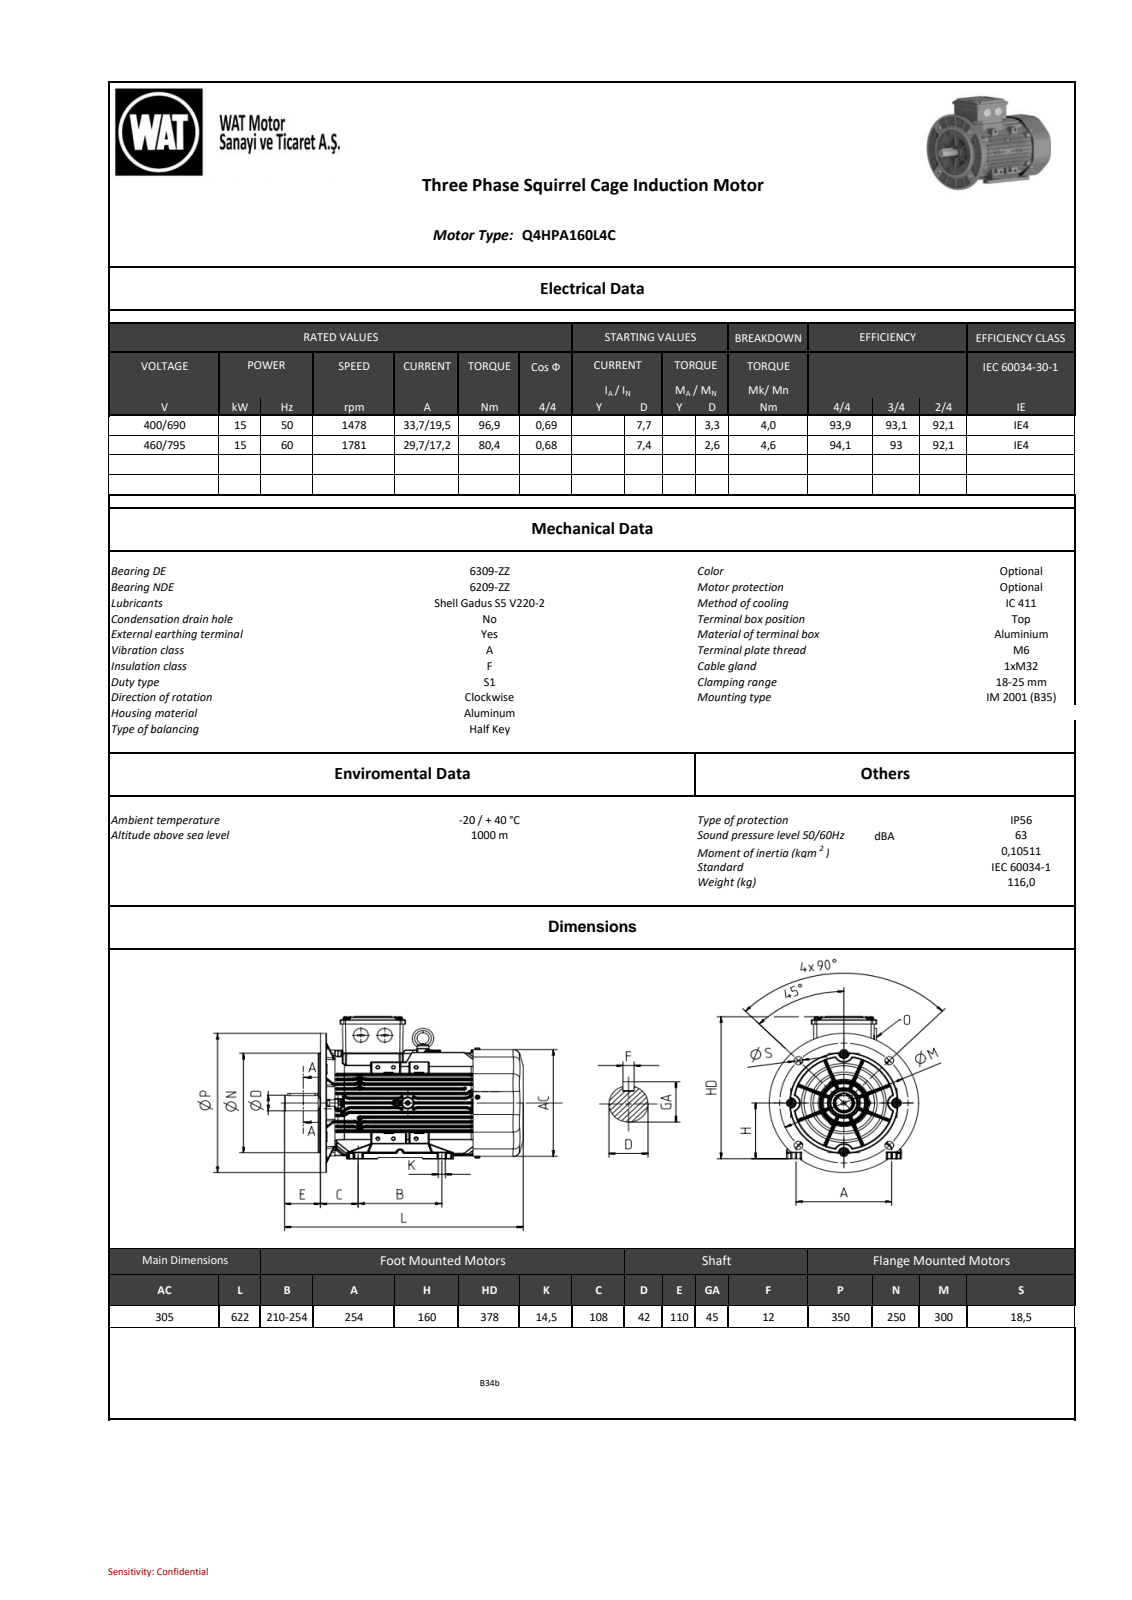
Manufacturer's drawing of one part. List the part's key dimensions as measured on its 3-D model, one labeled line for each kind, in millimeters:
Part name (STEP PRODUCT): AA_objects
STEP written by: SIEMENS PLM Software NX2206.8101 (AP203_CONFIGURATION_CONTROLLED_3D_DESIGN_OF_MECHANICAL_PARTS_AND_ASSEMBLIES_MIM_LF)
Units: millimetres
Bodies: 0 solids, 8586 faces (2343 planar, 3221 cylindrical, 3022 other)
Overall size (bounding box): 618.92 × 392.75 × 350
Round holes (diameter × count): ⌀15 ×4, ⌀10 ×1, ⌀14 ×1, ⌀17 ×1, ⌀72 ×1, ⌀85.63 ×1, ⌀94 ×1, ⌀114 ×1, ⌀134 ×1, ⌀154 ×1, ⌀174 ×1, ⌀194 ×1
Round bosses / shafts (diameter × count): ⌀16 ×4, ⌀10 ×4, ⌀8 ×4, ⌀38 ×2, ⌀272.5 ×1, ⌀250 ×1, ⌀178 ×1, ⌀158 ×1
Partial cylindrical surfaces — rounded edges, fillets, slot ends (radius × count): R0.5 ×657, R1 ×644, R2 ×134, R1.5 ×114, R4 ×104, R5 ×68, R2.5 ×43, R3 ×28
Main face-to-face distances: 144, 168, 120, 11.92, 9.62, 14.77, 168.39, 158.77, 24.39, 11.85
Hole centre spacings: 142.5, 201.53, 285, 0.43, 142.16, 142.24, 142.35, 142.41
